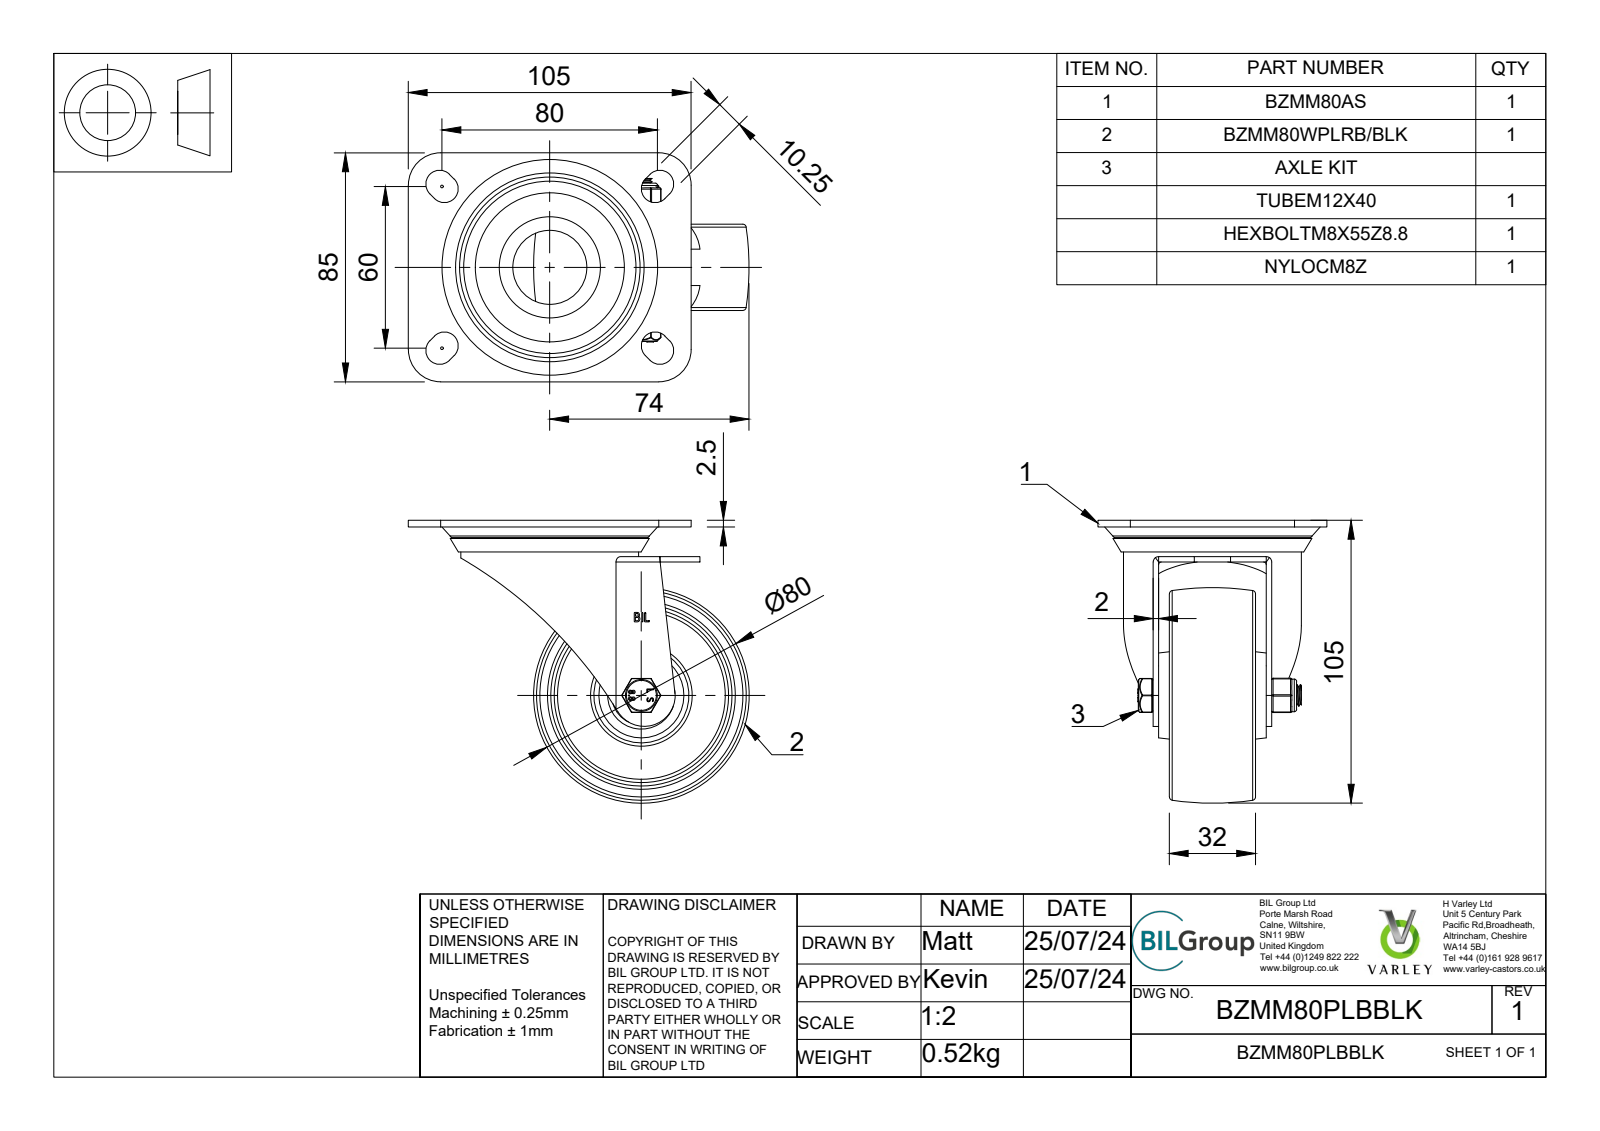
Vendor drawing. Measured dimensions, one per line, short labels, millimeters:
name: BZMM80PLBBLK v3; BZMM80AS - 2 v1; ZINC PLATED, PRESSED STEEL TOP PLATE 1; ZINC PLATED, PRESSED STEEL TOP PLATE 1 Geometry (+7 more)
written by: Autodesk Translation Framework v13.14.0.145 (AUTOMOTIVE_DESIGN)
unit: mm
bodies: 41 solids, 440 faces (171 planar, 147 cylindrical, 122 other)
size: 126.5 × 105 × 85
volume: 147 818 mm³; area: 86 303 mm²
holes: 2× ⌀0.66, 1× ⌀8, 1× ⌀8.2, 1× ⌀8.4, 1× ⌀8.6, 1× ⌀12, 1× ⌀19, 1× ⌀25, 1× ⌀27.5, 1× ⌀48, 1× ⌀62
bosses: 8× ⌀3.5, 1× ⌀66, 1× ⌀31.5, 1× ⌀22, 1× ⌀17.5, 1× ⌀12.1, 1× ⌀11.9, 1× ⌀11.5
rounds: 18× R0.5, 12× R0.25, 8× R5.12, 4× R0.33, 4× R0.64, 4× R1, 4× R12, 2× R0.63
face distances: 2.5, 2, 6, 19, 17, 23, 13, 25, 42, 10.5
hole spacings: 3.22, 2.49
